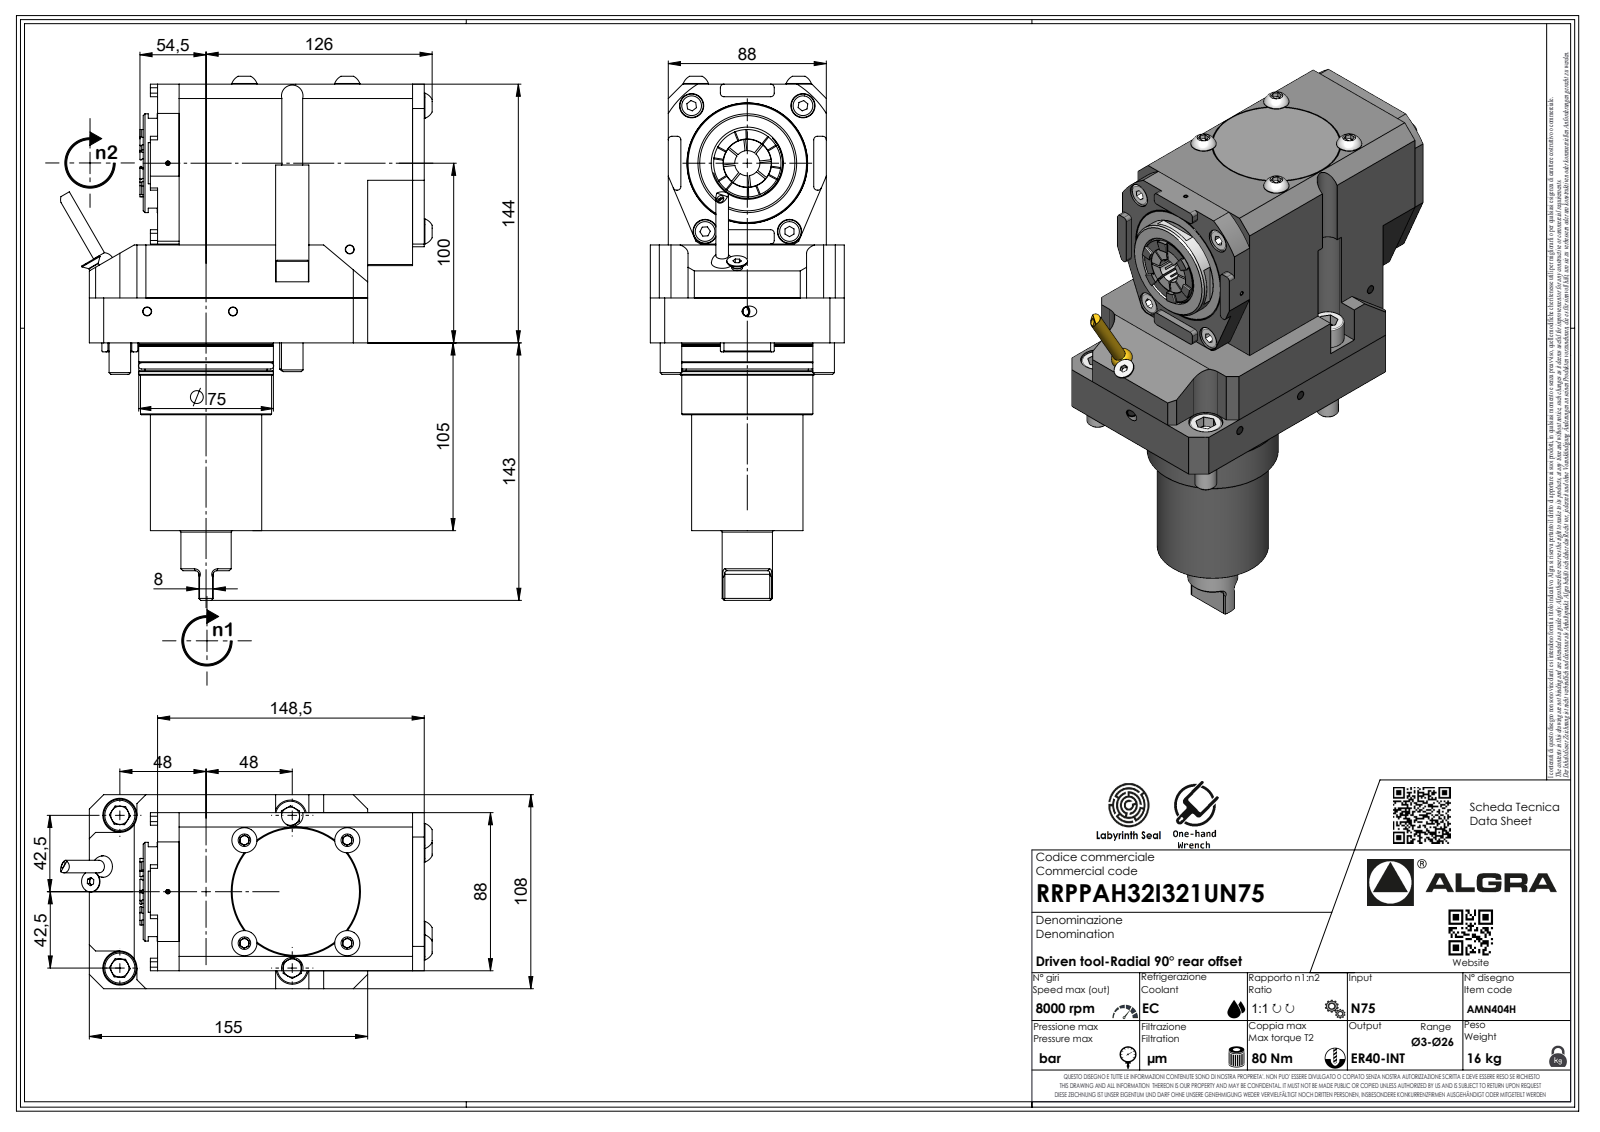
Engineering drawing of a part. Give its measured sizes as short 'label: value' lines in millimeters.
name: RRPPAH32I321UN75
written by: SolidWorks 2023 (AUTOMOTIVE_DESIGN)
unit: mm
bodies: 1 solid, 597 faces (364 planar, 98 cylindrical, 135 other)
size: 287.3 × 202.51 × 108
volume: 2 392 000 mm³; area: 145 063 mm²
holes: 1× ⌀2.1, 1× ⌀4, 1× ⌀12
bosses: 3× ⌀12, 1× ⌀75, 1× ⌀74.6, 1× ⌀73, 1× ⌀68, 1× ⌀62, 1× ⌀55, 1× ⌀28
rounds: 23× R2, 7× R0.33, 7× R0.52, 7× R3.7, 2× R1, 2× R9.25, 2× R9.5, 1× R0.21
face distances: 98, 10, 144, 88, 108, 31.5, 117, 54.5, 89.5, 155
